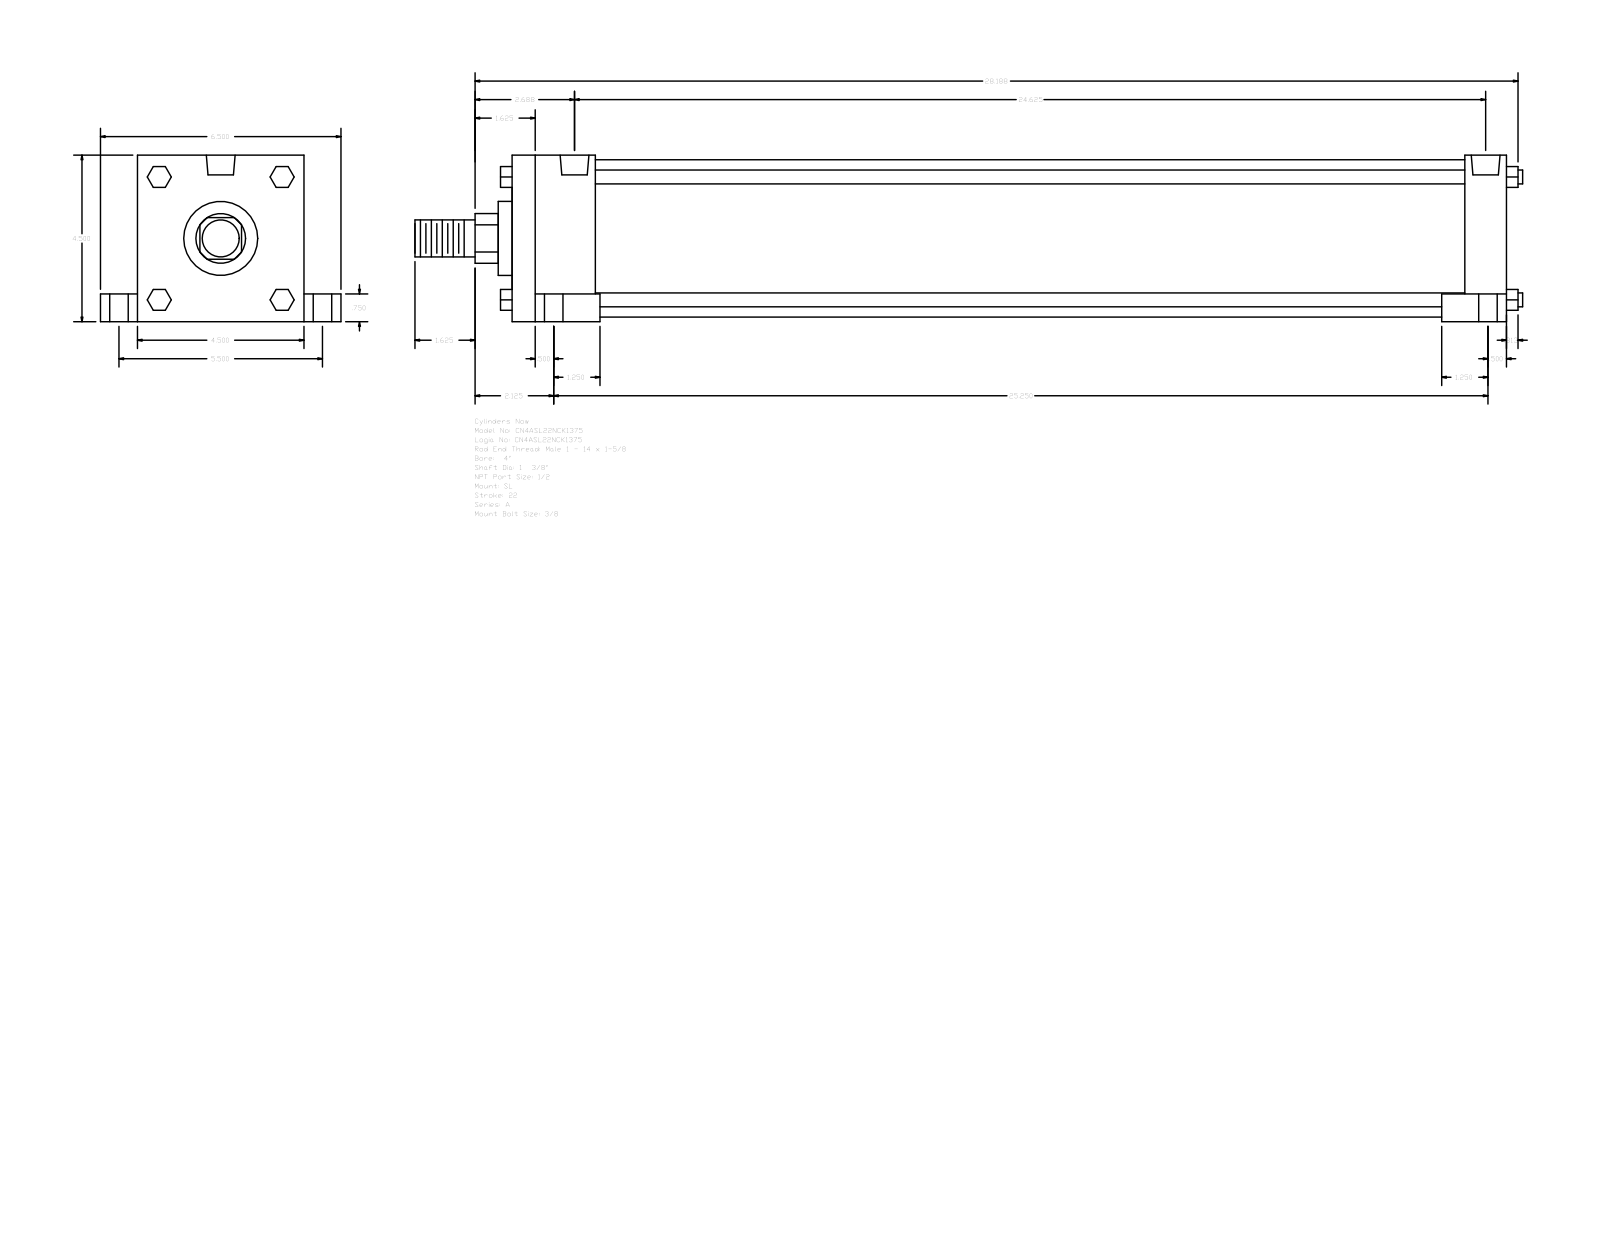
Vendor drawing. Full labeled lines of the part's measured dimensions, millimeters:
Part name (STEP PRODUCT): A_SL__0400_1.375
STEP written by: GSSL Pune (CONFIG_CONTROL_DESIGN)
Units: millimetres
Bodies: 0 solids, 150 faces (114 planar, 36 cylindrical, 0 other)
Overall size (bounding box): 760.41 × 165.1 × 114.3
Round holes (diameter × count): ⌀8.73 ×4, ⌀12.7 ×4, ⌀19.05 ×4, ⌀19.77 ×2
Round bosses / shafts (diameter × count): ⌀9.53 ×4, ⌀107.95 ×1, ⌀50.8 ×1, ⌀34.92 ×1, ⌀25.4 ×1
Partial cylindrical surfaces — rounded edges, fillets, slot ends (radius × count): R17.06 ×1
Main face-to-face distances: 114.3, 682.62, 57.15, 28.57, 25.4, 625.47, 654.05, 596.9, 139.7, 19.05
Hole centre spacings: 3.18, 69.87, 70.01, 71.29, 72, 139.7, 619.12, 622.3
